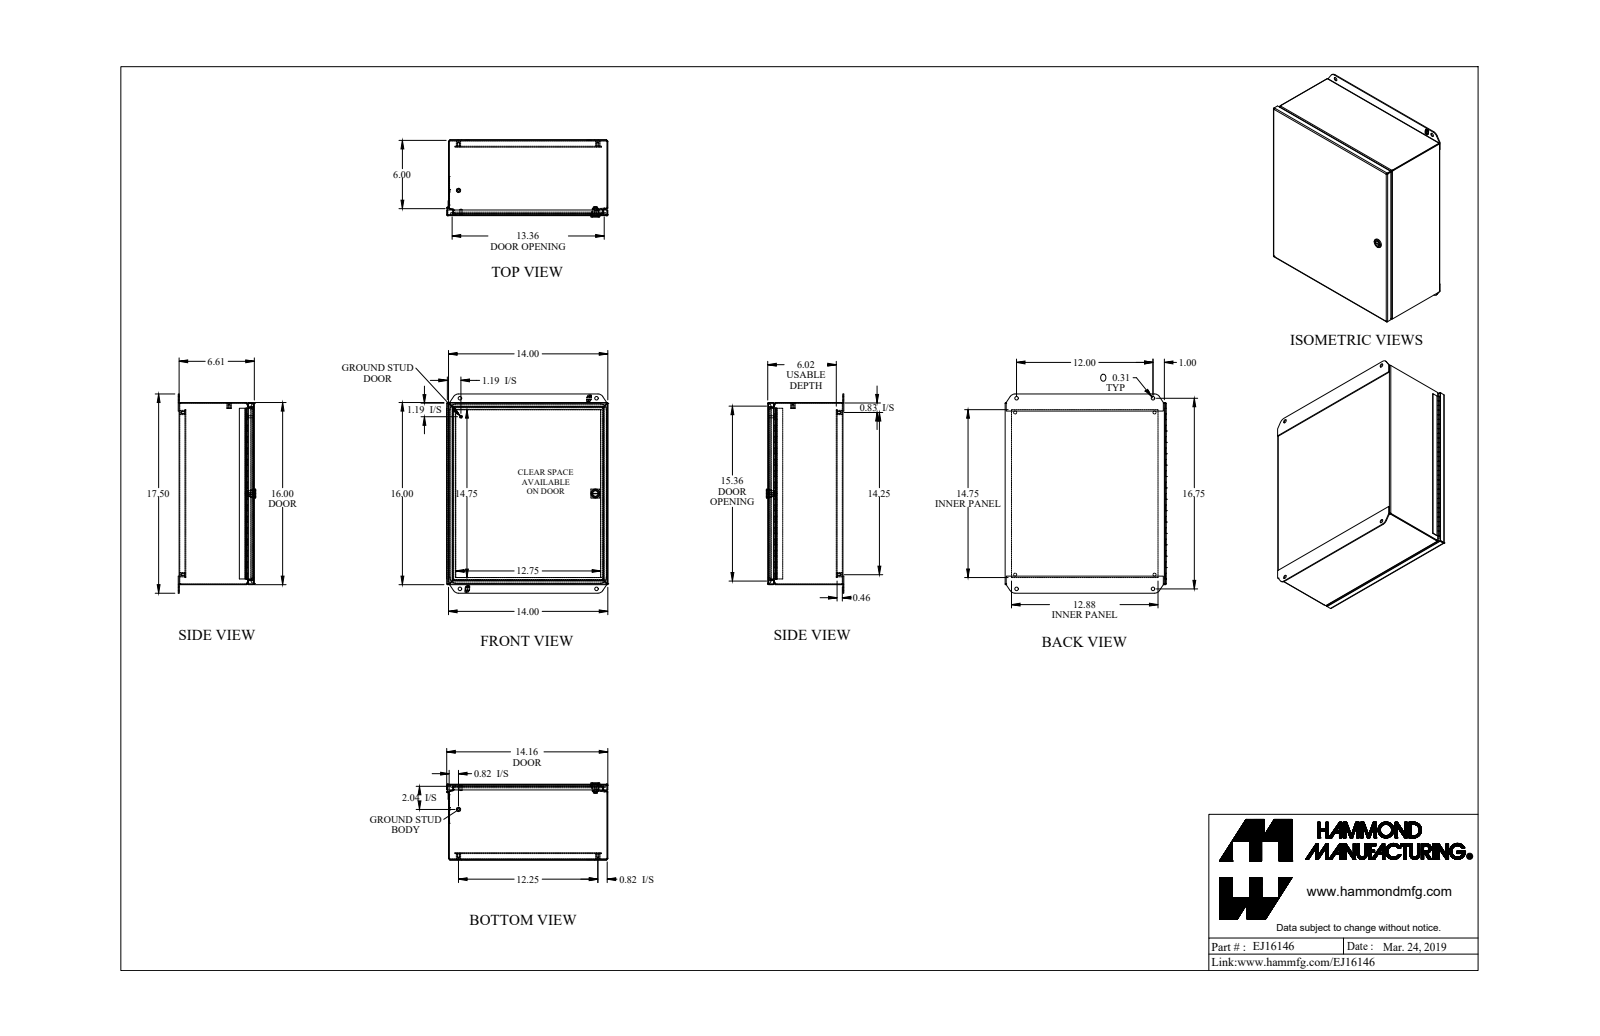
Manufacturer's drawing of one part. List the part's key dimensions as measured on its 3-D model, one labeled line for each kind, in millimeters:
Part name (STEP PRODUCT): EJ16146_Default
STEP written by: SolidWorks 2019 (CONFIG_CONTROL_DESIGN)
Units: millimetres
Bodies: 16 solids, 771 faces (425 planar, 254 cylindrical, 92 other)
Overall size (bounding box): 444.5 × 359.8 × 172.8
Volume: 1 194 000 mm³ · Surface area: 1 550 000 mm²
Round holes (diameter × count): ⌀4 ×5, ⌀6.7 ×4, ⌀8 ×4, ⌀1.3 ×1, ⌀13.1 ×1
Round bosses / shafts (diameter × count): ⌀9.5 ×5, ⌀20 ×1, ⌀13.6 ×1, ⌀12.6 ×1, ⌀11 ×1, ⌀6.4 ×1, ⌀4.8 ×1, ⌀2.5 ×1
Partial cylindrical surfaces — rounded edges, fillets, slot ends (radius × count): R0.7 ×16, R2.2 ×16, R7.1 ×10, R6.4 ×4, R12.7 ×4, R12.7 ×4, R1.5 ×2, R13.7 ×2
Main face-to-face distances: 1.4, 166.5, 1.8, 15, 167.9, 165, 11.7, 13.1, 154.8, 153.3
Hole centre spacings: 31.9, 393.7, 499.8, 362, 309.6, 181.1, 212.7, 304.8
